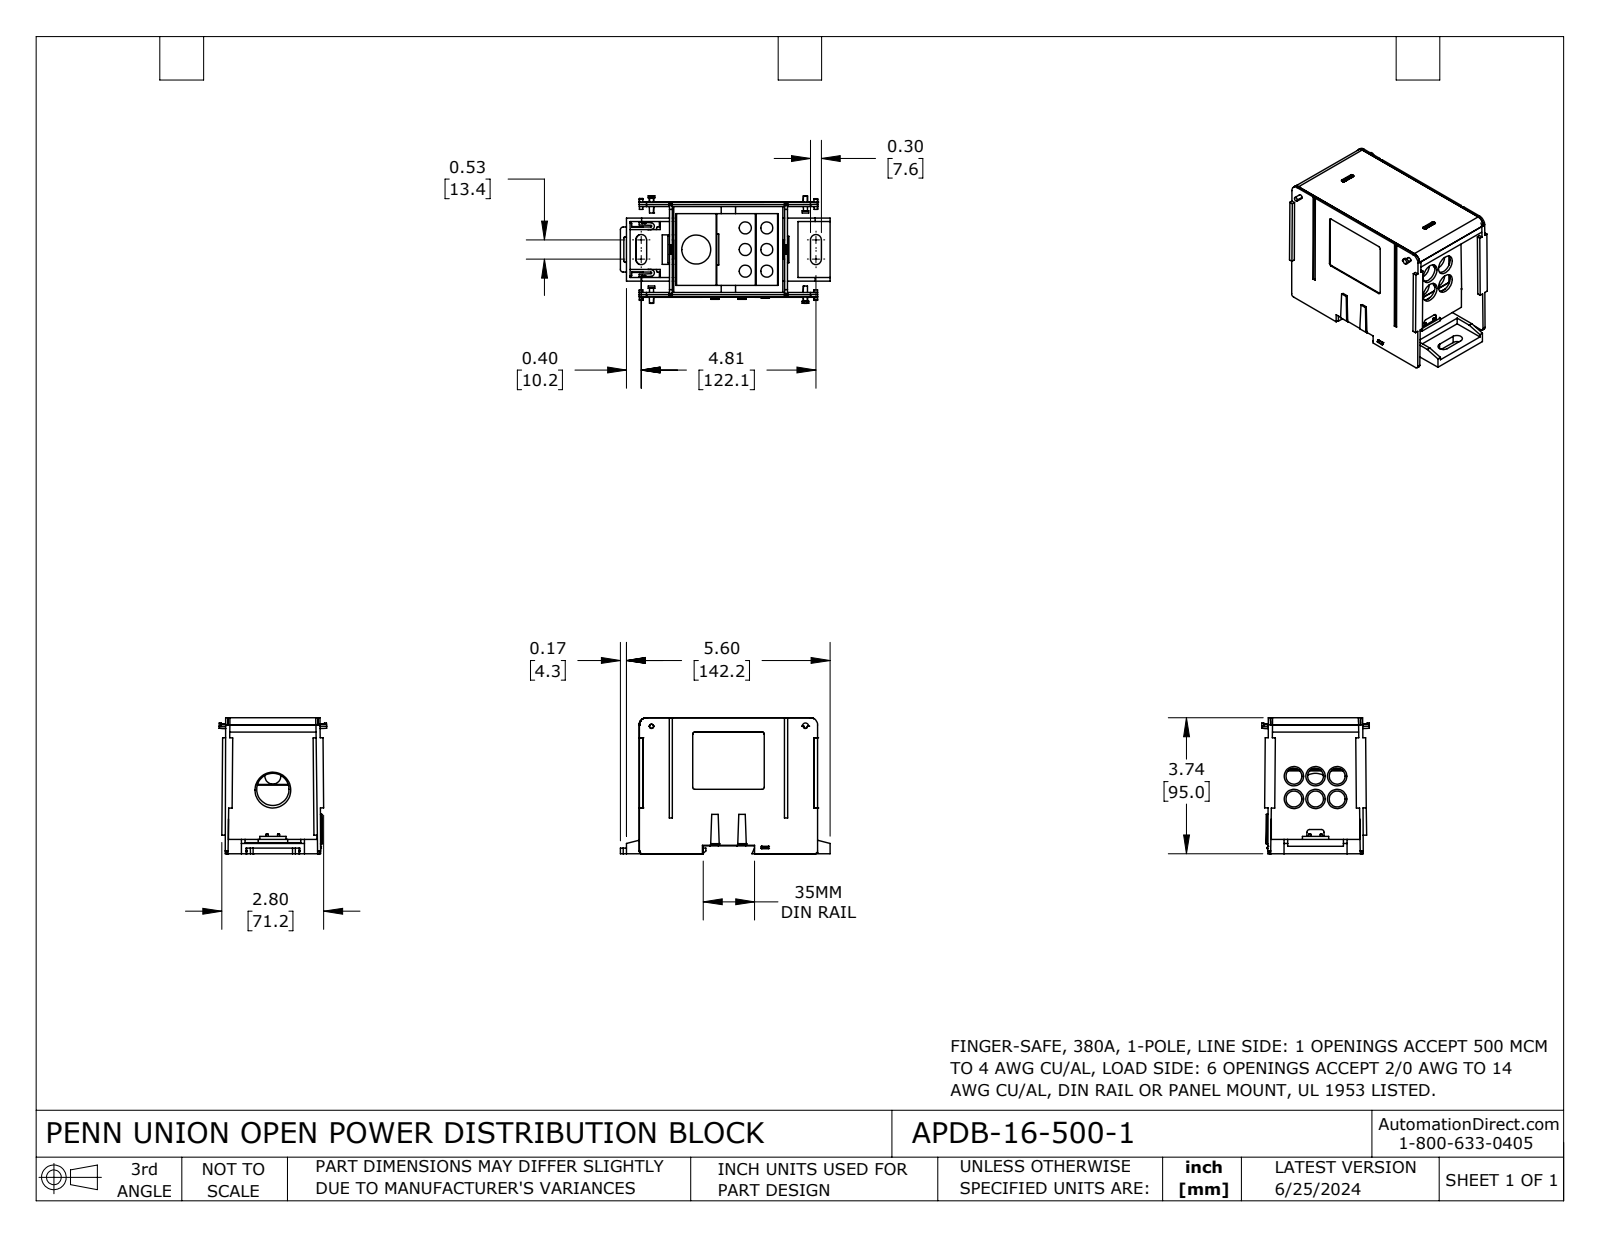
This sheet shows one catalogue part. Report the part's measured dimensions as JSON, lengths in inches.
{"part_name": "APDB-16-500-1", "step_written_by": "SolidWorks 2023 (CONFIG_CONTROL_DESIGN)", "units": "inches", "bodies": {"solids": 10, "faces": 798, "planar": 554, "cylindrical": 173, "other": 71}, "overall_size": [5.77, 3.741, 2.955], "volume_in3": 18.77, "surface_area_in2": 231, "round_holes": [[0.437, 6], [0.531, 6], [0.33, 5], [0.213, 1], [0.33, 1], [0.798, 1], [0.886, 1], [0.984, 1]], "partial_cylinders_radius": [[0.02, 32], [0.059, 18], [0.039, 10], [0.079, 10], [0.197, 10], [0.012, 6], [0.089, 4], [0.15, 4]], "face_to_face_distances": [0.079, 3.169, 2.54, 0.071, 2.469, 0.02, 3.091, 3.248, 1.201, 3.67], "hole_center_spacings": [0.594, 0.839, 0.863, 1.189, 0.593, 0.626, 0.643, 0.65]}
